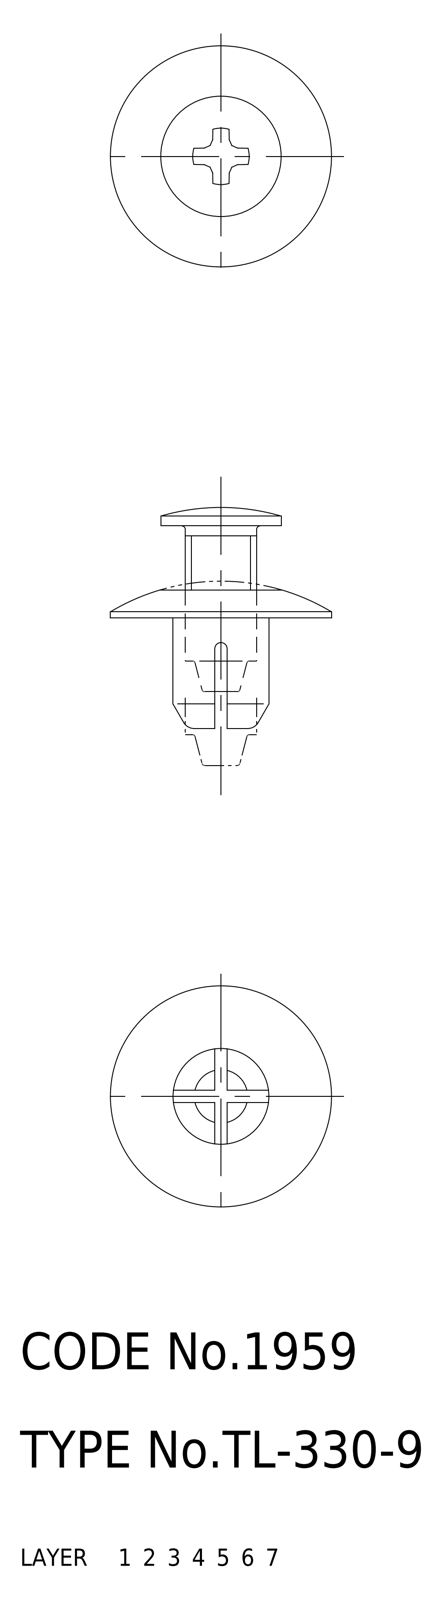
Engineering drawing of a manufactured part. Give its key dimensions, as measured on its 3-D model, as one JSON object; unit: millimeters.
{"part_name": "pin; grommet; TL_330_9_10979_36", "step_written_by": "CADfix (AUTOMOTIVE_DESIGN)", "units": "millimeters", "bodies": {"solids": 2, "faces": 84, "planar": 0, "cylindrical": 0, "other": 84}, "overall_size": [18, 18, 17.95], "volume_mm3": 823, "surface_area_mm2": 1386}
